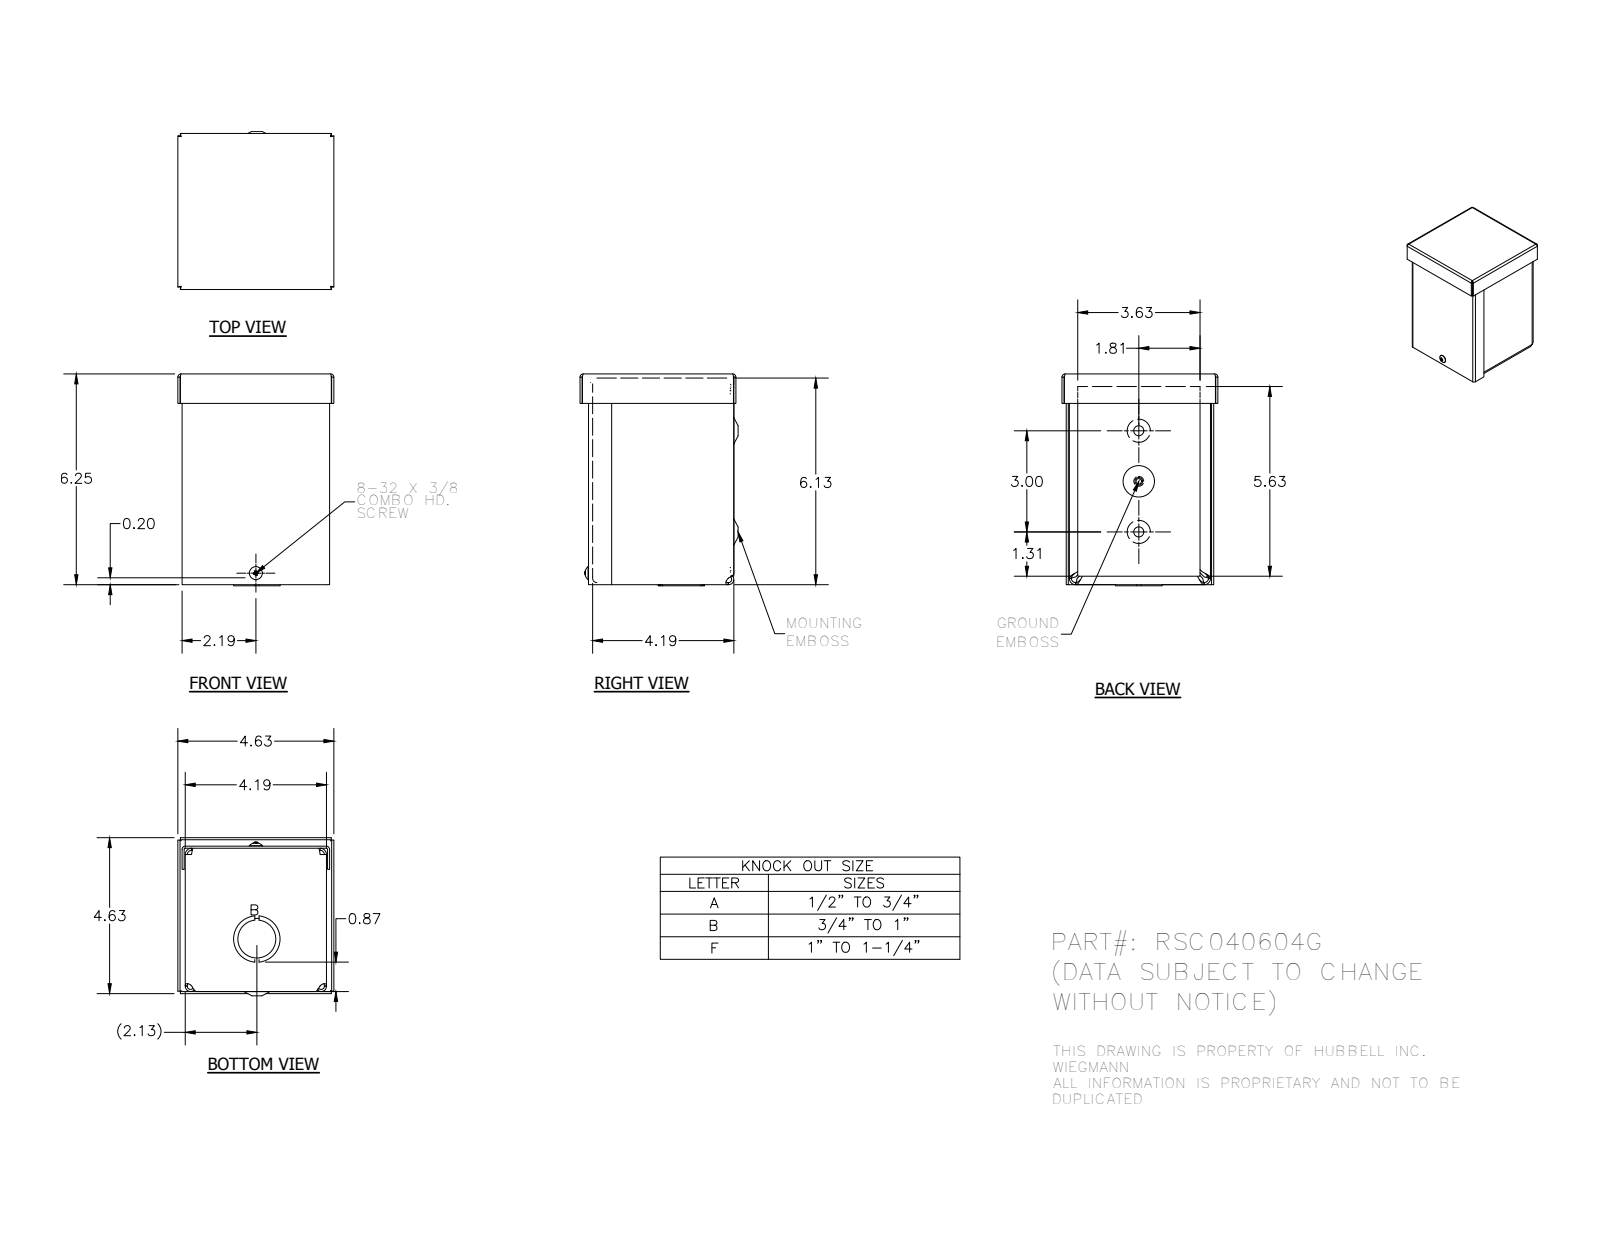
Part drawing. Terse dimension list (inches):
name: RSC040604G_WRAP; RSC0406G_LID; RSC0404G_CAP; RSC0604G_BKP (+3 more)
written by: Autodesk Inventor 2014 (AUTOMOTIVE_DESIGN)
unit: in
bodies: 5 solids, 348 faces (155 planar, 76 cylindrical, 117 other)
size: 6.281 × 4.689 × 4.625
volume: 12.39 in³; area: 408.4 in²
holes: 2× ⌀0.3, 2× ⌀0.313, 1× ⌀0.148, 1× ⌀0.165, 1× ⌀1.125, 1× ⌀1.375
bosses: 1× ⌀0.384, 1× ⌀0.228, 1× ⌀0.164
rounds: 8× R0.125, 8× R0.187, 6× R0.031, 6× R0.093, 4× R0.01, 4× R0.055, 4× R0.062, 4× R0.094
face distances: 0.062, 0.062, 4.126, 4.249, 4.063, 4.188, 0.124, 6.126, 4.187, 0.063
hole spacings: 1.5, 1.093, 1.22, 2.593, 2.72, 3, 4.093, 4.22
